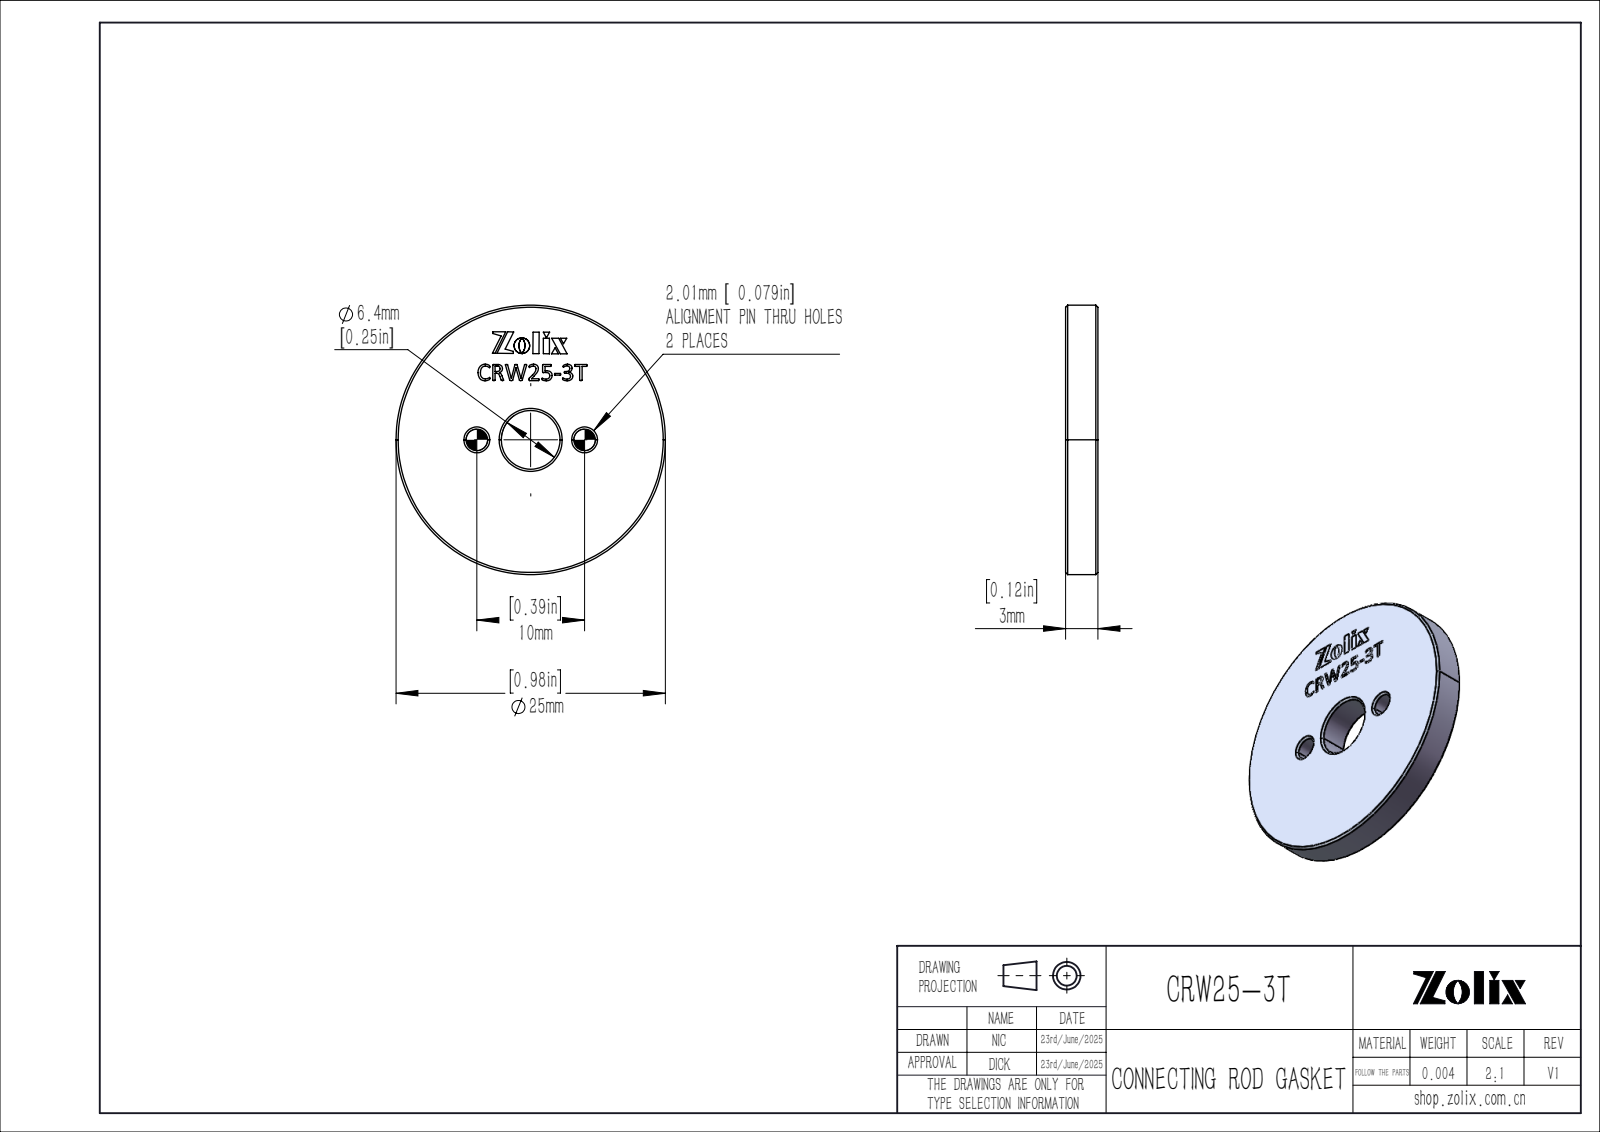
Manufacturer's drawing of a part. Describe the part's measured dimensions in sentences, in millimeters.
The part is named "CRW25-3T". Its 3-D file was written by "SolidWorks 2020 (CONFIG_CONTROL_DESIGN)". It is 1 solid with 330 faces: 222 planar, 8 cylindrical and 100 other. Overall it measures 25 by 25 by 3 millimeters. Its volume is 1 379 cubic millimeters and its surface area 1 224 square millimeters. Round holes: 2 of diameter 2, 1 of diameter 5.45. Round bosses or shafts: 1 of diameter 25. The main face-to-face distances are 3, 2.98, 0.56, 2, 8.07, 1.44, 0.66, 0.57, 1.32, 0.96. The hole center spacings are 5, 10.
